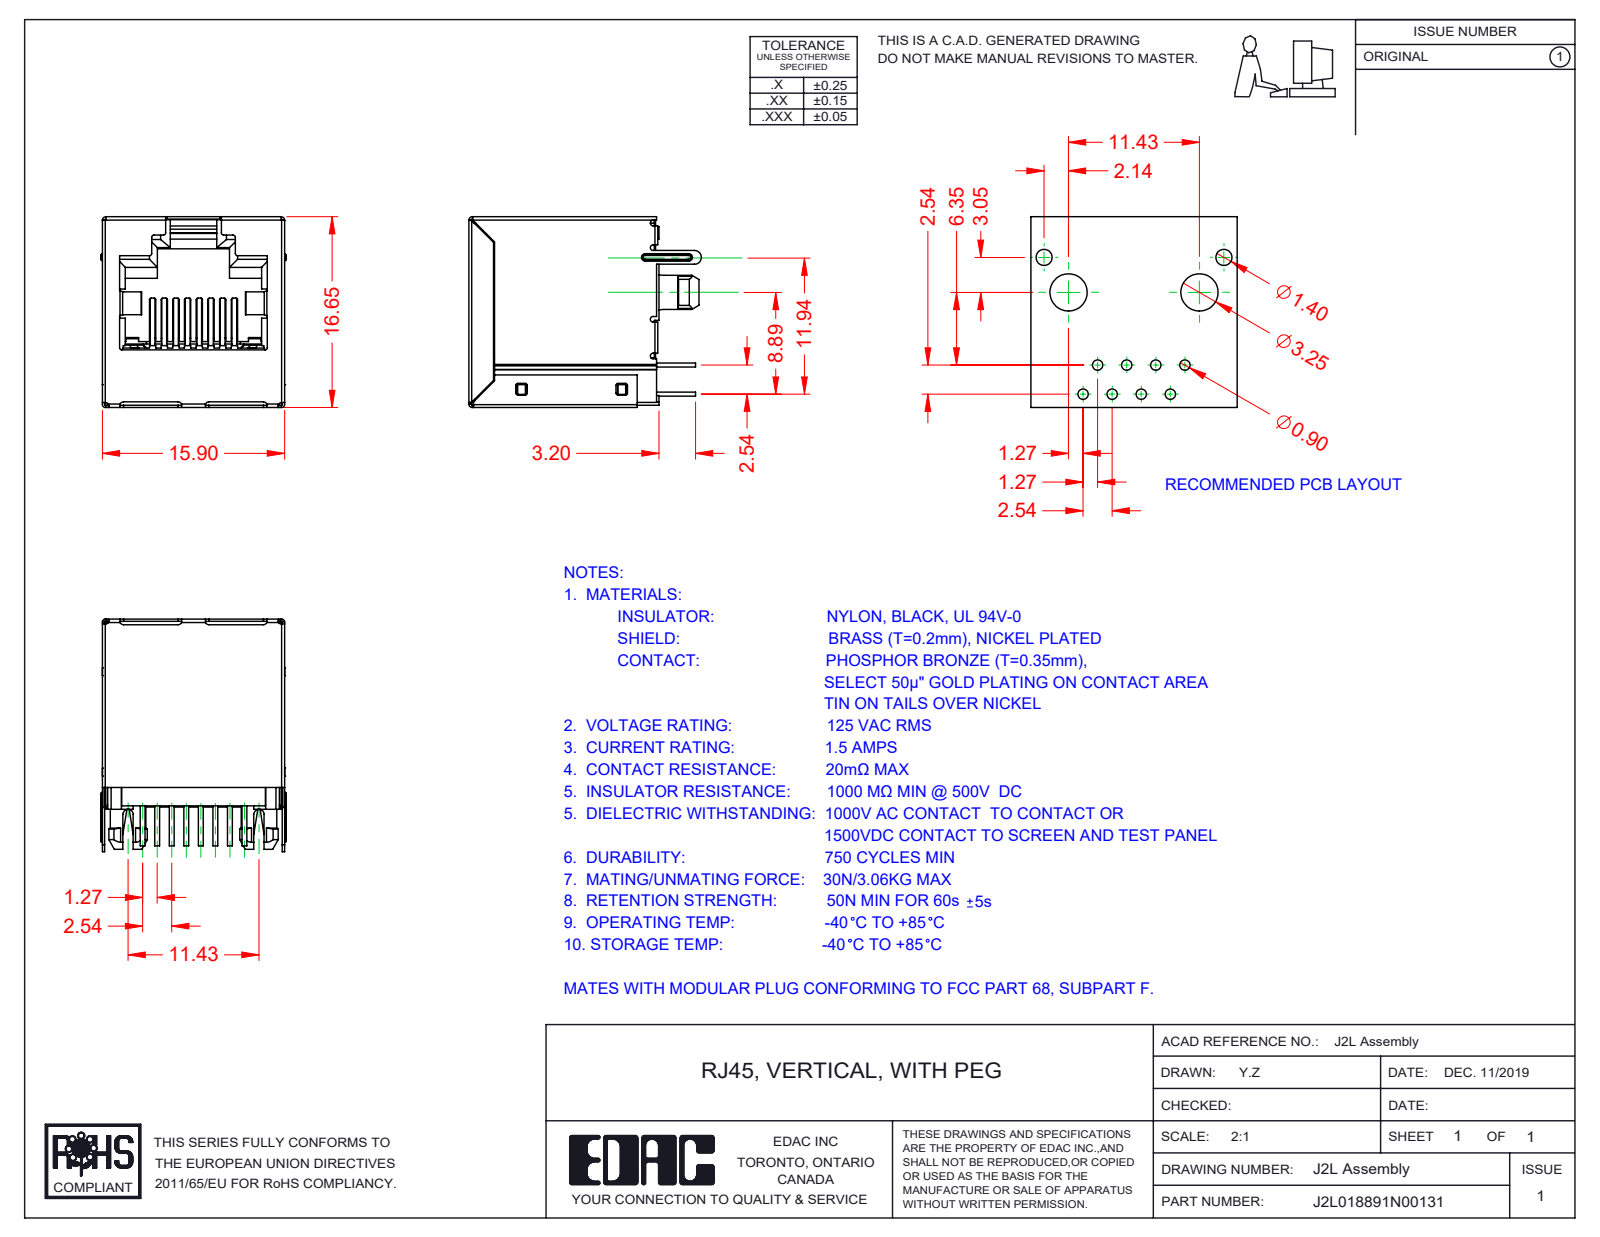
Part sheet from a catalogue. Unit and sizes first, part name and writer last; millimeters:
Units: millimetres
Overall size (bounding box): 20.3 × 16.65 × 16.2
Round bosses / shafts (diameter × count): ⌀3.1 ×2, ⌀1.1 ×2
Partial cylindrical surfaces — rounded edges, fillets, slot ends (radius × count): R0.15 ×64, R0.25 ×20, R0.2 ×16, R0.3 ×14, R0.35 ×9, R0.1 ×8, R0.28 ×4, R0.5 ×3
Main face-to-face distances: 15.45, 15.7, 16.45, 16.2, 16.4, 15.65, 16.25, 15.9, 15.5, 1.2
Volume: 2 717 mm³ · Surface area: 6 473 mm²
Bodies: 11 solids, 1125 faces (778 planar, 284 cylindrical, 63 other)
Part name (STEP PRODUCT): 2L Contacts; 2L Shield; RJ2L018891N00131; 2L Contact Lock (+1 more)
STEP written by: SolidWorks 2016 (CONFIG_CONTROL_DESIGN)
